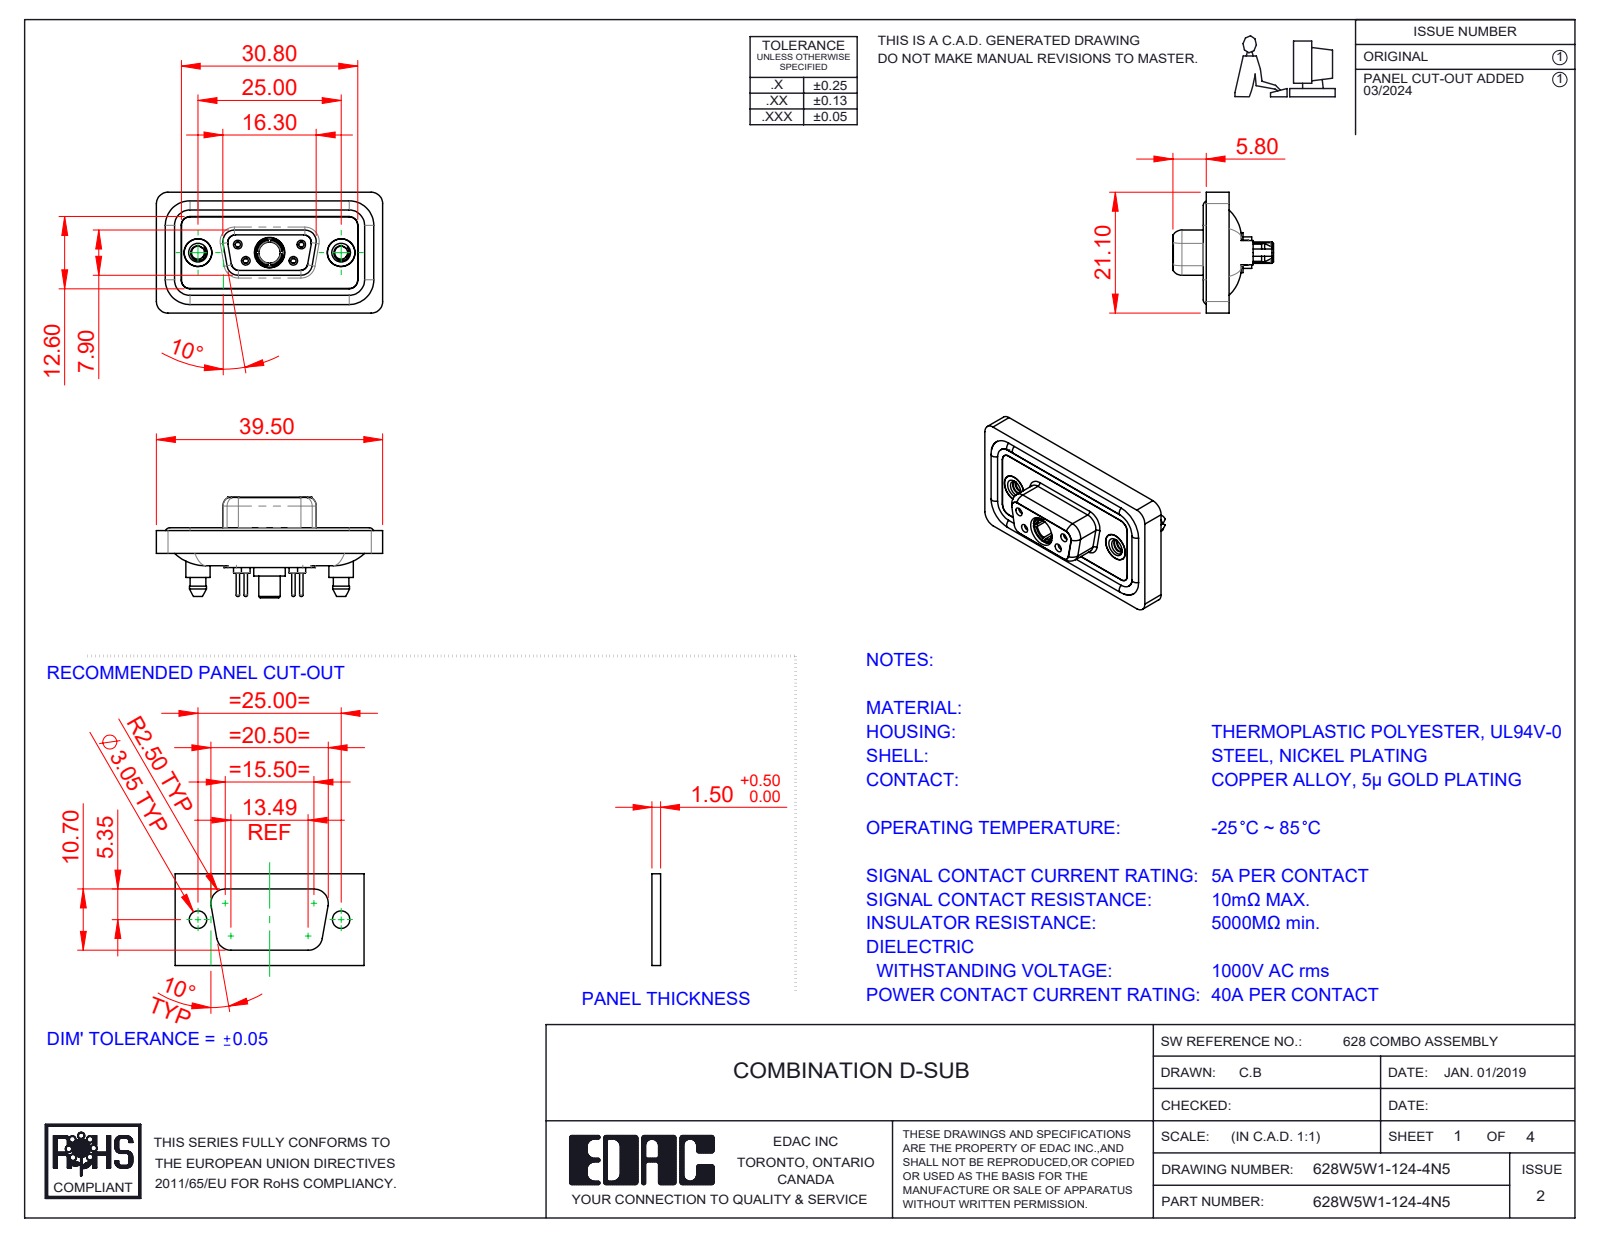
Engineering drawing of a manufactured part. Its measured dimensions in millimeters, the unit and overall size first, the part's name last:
Units: millimetres
Overall size (bounding box): 39.5 × 21.1 × 17.55
Round holes (diameter × count): ⌀0.9 ×4, ⌀1.1 ×4, ⌀1.5 ×4, ⌀2 ×4, ⌀4.85 ×3, ⌀1.6 ×2, ⌀1.7 ×2, ⌀2.26 ×2, ⌀4 ×2, ⌀4.05 ×2, ⌀5 ×2, ⌀3.7 ×1
Round bosses / shafts (diameter × count): ⌀1.6 ×6, ⌀2.2 ×4, ⌀0.6 ×4, ⌀5.4 ×2, ⌀4.95 ×2, ⌀4.8 ×2, ⌀4.25 ×2, ⌀5.5 ×1
Partial cylindrical surfaces — rounded edges, fillets, slot ends (radius × count): R1.5 ×24, R2 ×18, R1.6 ×10, R1.35 ×8, R0.25 ×4, R0.5 ×4, R0.6 ×4, R0.65 ×4
Main face-to-face distances: 0.4, 2.9, 1.1, 1.8, 1.6, 0.5, 5.65, 7.45, 5.35, 3.6
Hole centre spacings: 3.16, 5.72, 7.1, 12.5, 18.1, 4.39, 4.4, 8.31
Volume: 4 919 mm³ · Surface area: 7 979 mm²
Bodies: 13 solids, 730 faces (210 planar, 319 cylindrical, 201 other)
Part name (STEP PRODUCT): 628Combo Waterproof Housing_09 Contacts; 628Combo Shell Rear_09 Contacts; 628Combo Threaded Boardlock_5; 628Combo Contact Row 2_24 (+5 more)
STEP written by: SolidWorks 2023 (CONFIG_CONTROL_DESIGN)
